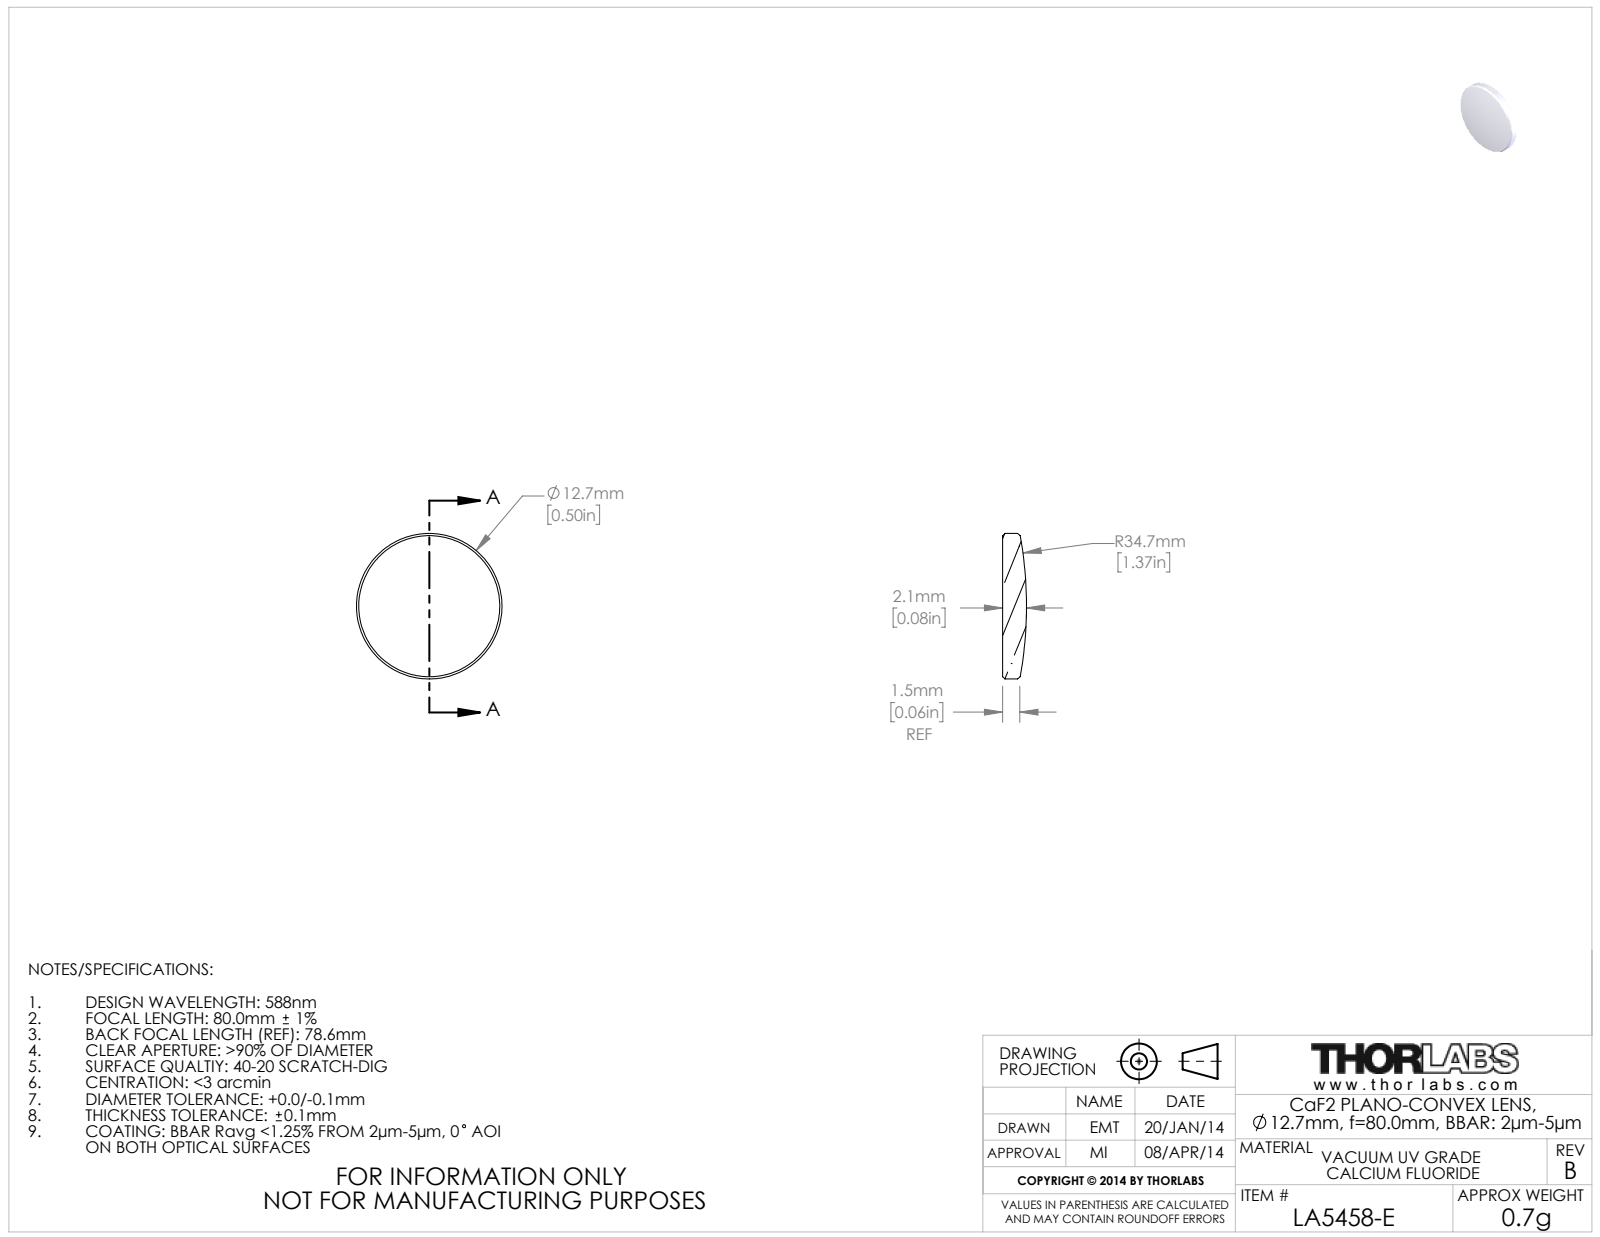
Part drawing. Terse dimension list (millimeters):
name: 20130-E0W
written by: SolidWorks 2018 (CONFIG_CONTROL_DESIGN)
unit: mm
bodies: 1 solid, 9 faces (1 planar, 2 cylindrical, 6 other)
size: 12.7 × 12.7 × 2.08
volume: 225 mm³; area: 306 mm²
bosses: 1× ⌀12.7
